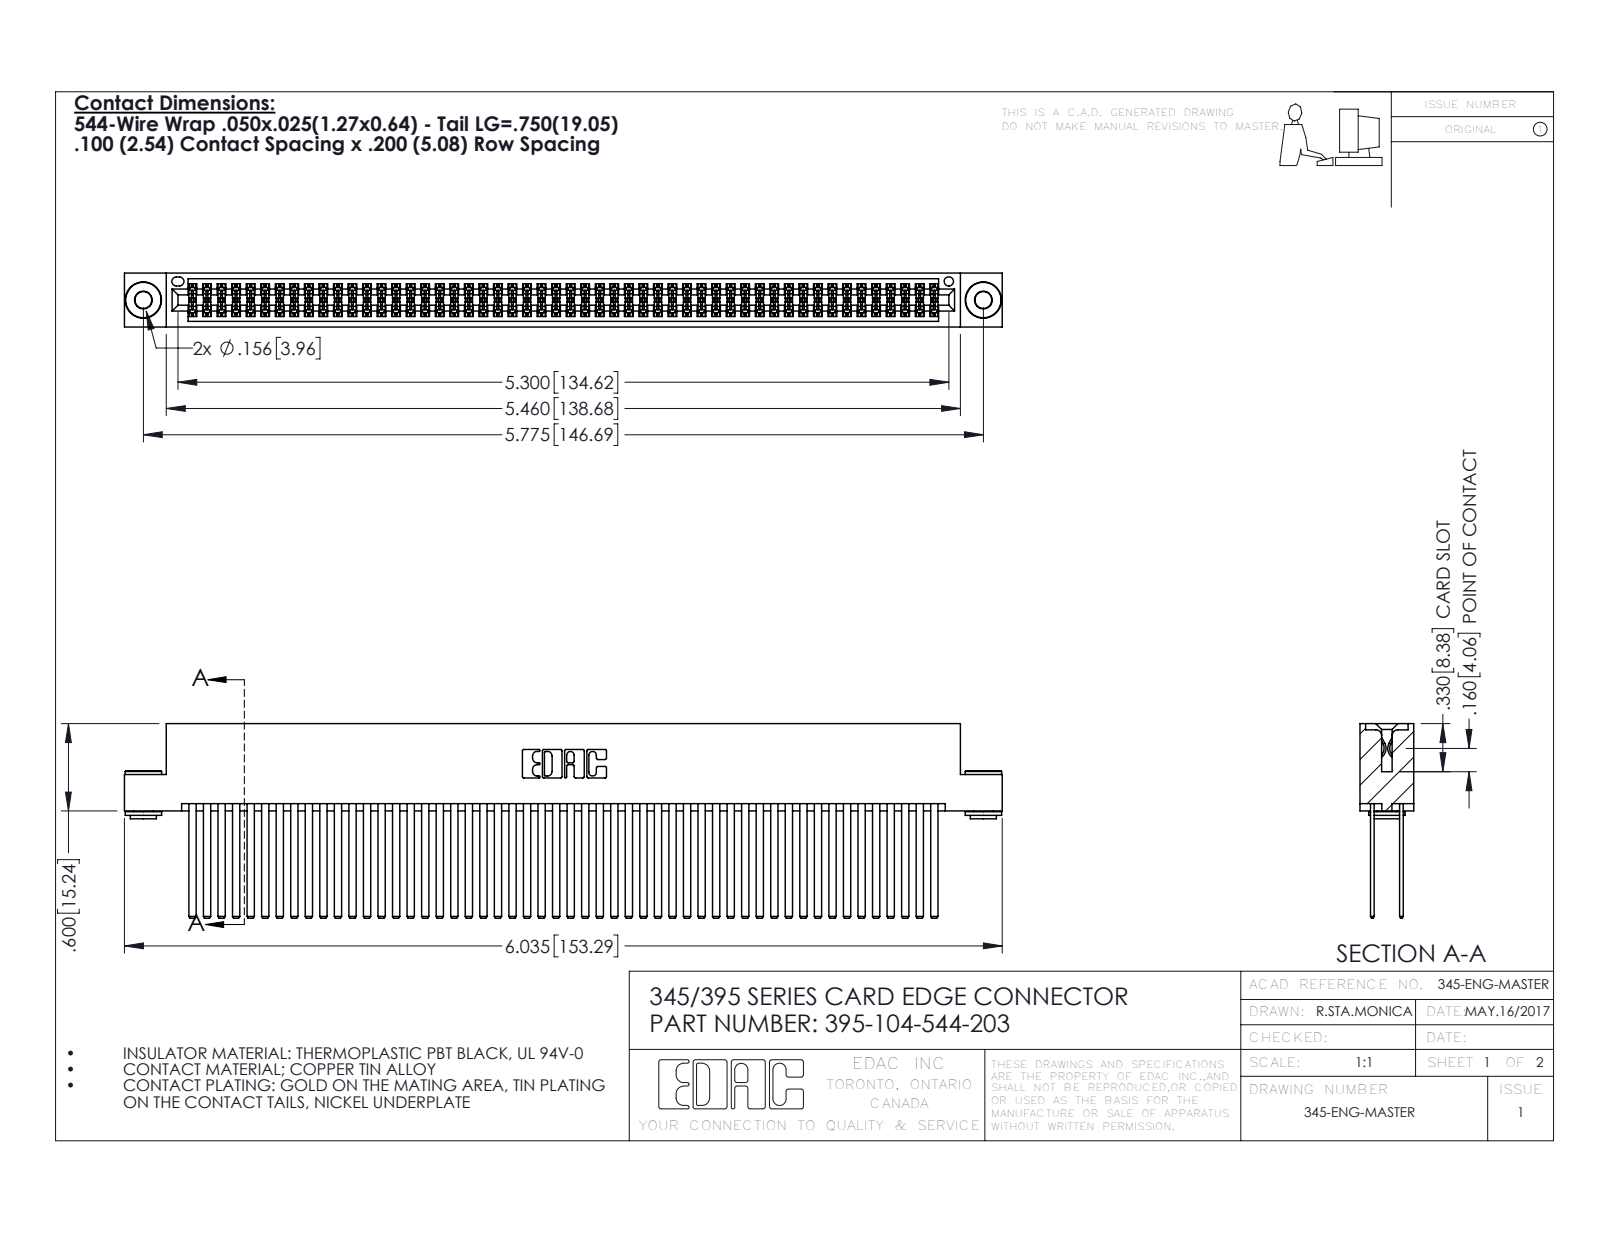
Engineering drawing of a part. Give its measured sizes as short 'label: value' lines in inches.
name: 345 Part_Flush Mounting Lugs - 0.156 Dia-TH; 395-104-544-203; 345-250-002_345-250-002-102; 345-292-001_345-293-144
written by: SolidWorks 2016 (CONFIG_CONTROL_DESIGN)
unit: in
bodies: 107 solids, 4740 faces (3106 planar, 1626 cylindrical, 8 other)
size: 6.035 × 1.337 × 0.37
volume: 1.004 in³; area: 44.96 in²
holes: 2× ⌀0.116, 2× ⌀0.156, 1× ⌀0.064
bosses: 2× ⌀0.25, 2× ⌀0.18, 2× ⌀0.136
rounds: 156× R0.006, 22× R0.01, 6× R0.007, 6× R0.031, 3× R0.026, 2× R0.014, 2× R0.019, 2× R0.022
face distances: 0.2, 0.025, 0.072, 0.098, 0.272, 0.298, 0.225, 0.175, 0.37, 0.05
hole spacings: 0.27, 5.539, 5.775
